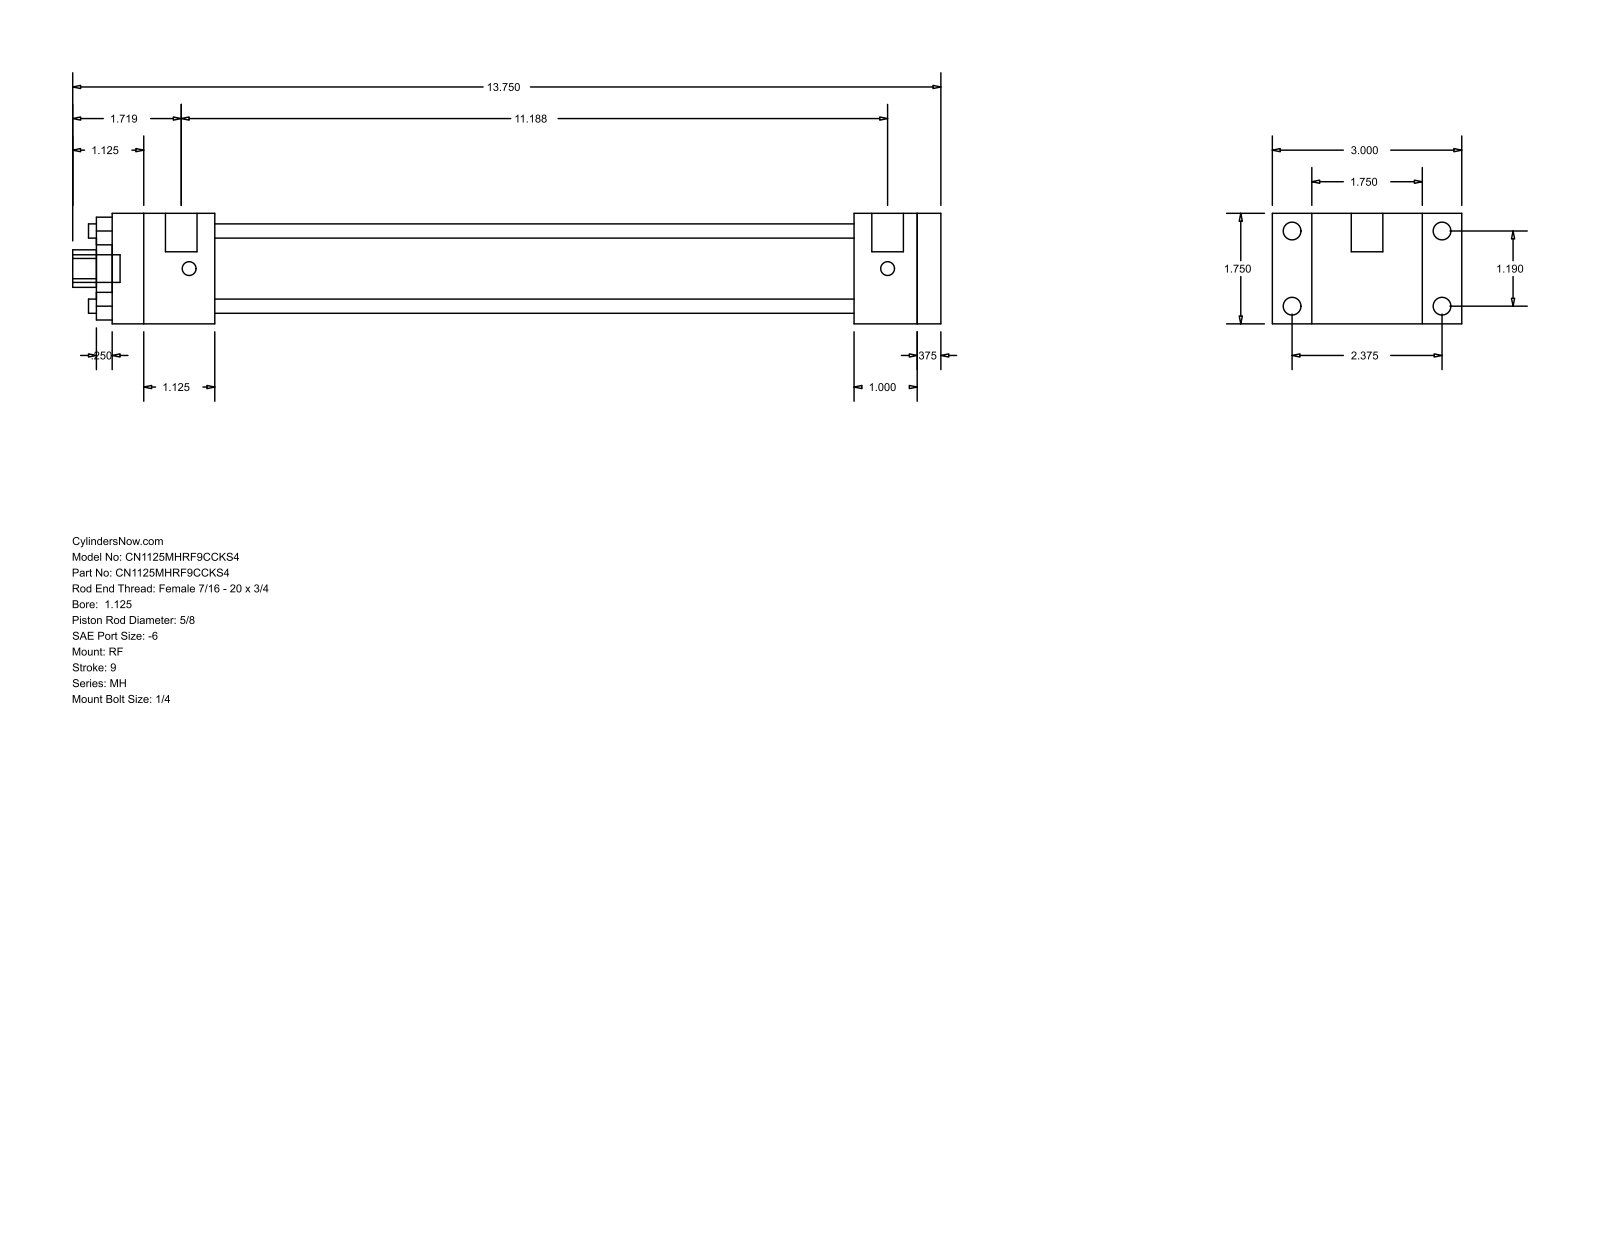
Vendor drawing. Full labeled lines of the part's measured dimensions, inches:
Part name (STEP PRODUCT): MH_RF__0112_0.625
STEP written by: GSSL Pune (CONFIG_CONTROL_DESIGN)
Units: inches
Bodies: 0 solids, 92 faces (64 planar, 28 cylindrical, 0 other)
Overall size (bounding box): 13.75 × 3 × 1.75
Round holes (diameter × count): ⌀0.225 ×4, ⌀0.625 ×1, ⌀1.125 ×1, ⌀1.375 ×1
Round bosses / shafts (diameter × count): ⌀0.281 ×4, ⌀0.219 ×4, ⌀0.5 ×2, ⌀0.437 ×1
Partial cylindrical surfaces — rounded edges, fillets, slot ends (radius × count): R0.297 ×1
Main face-to-face distances: 1.75, 0.375, 0.625, 11.125, 11.5, 10.125, 1, 1.375, 1.625, 11.75
Hole centre spacings: 0.841, 1.19, 1.683
